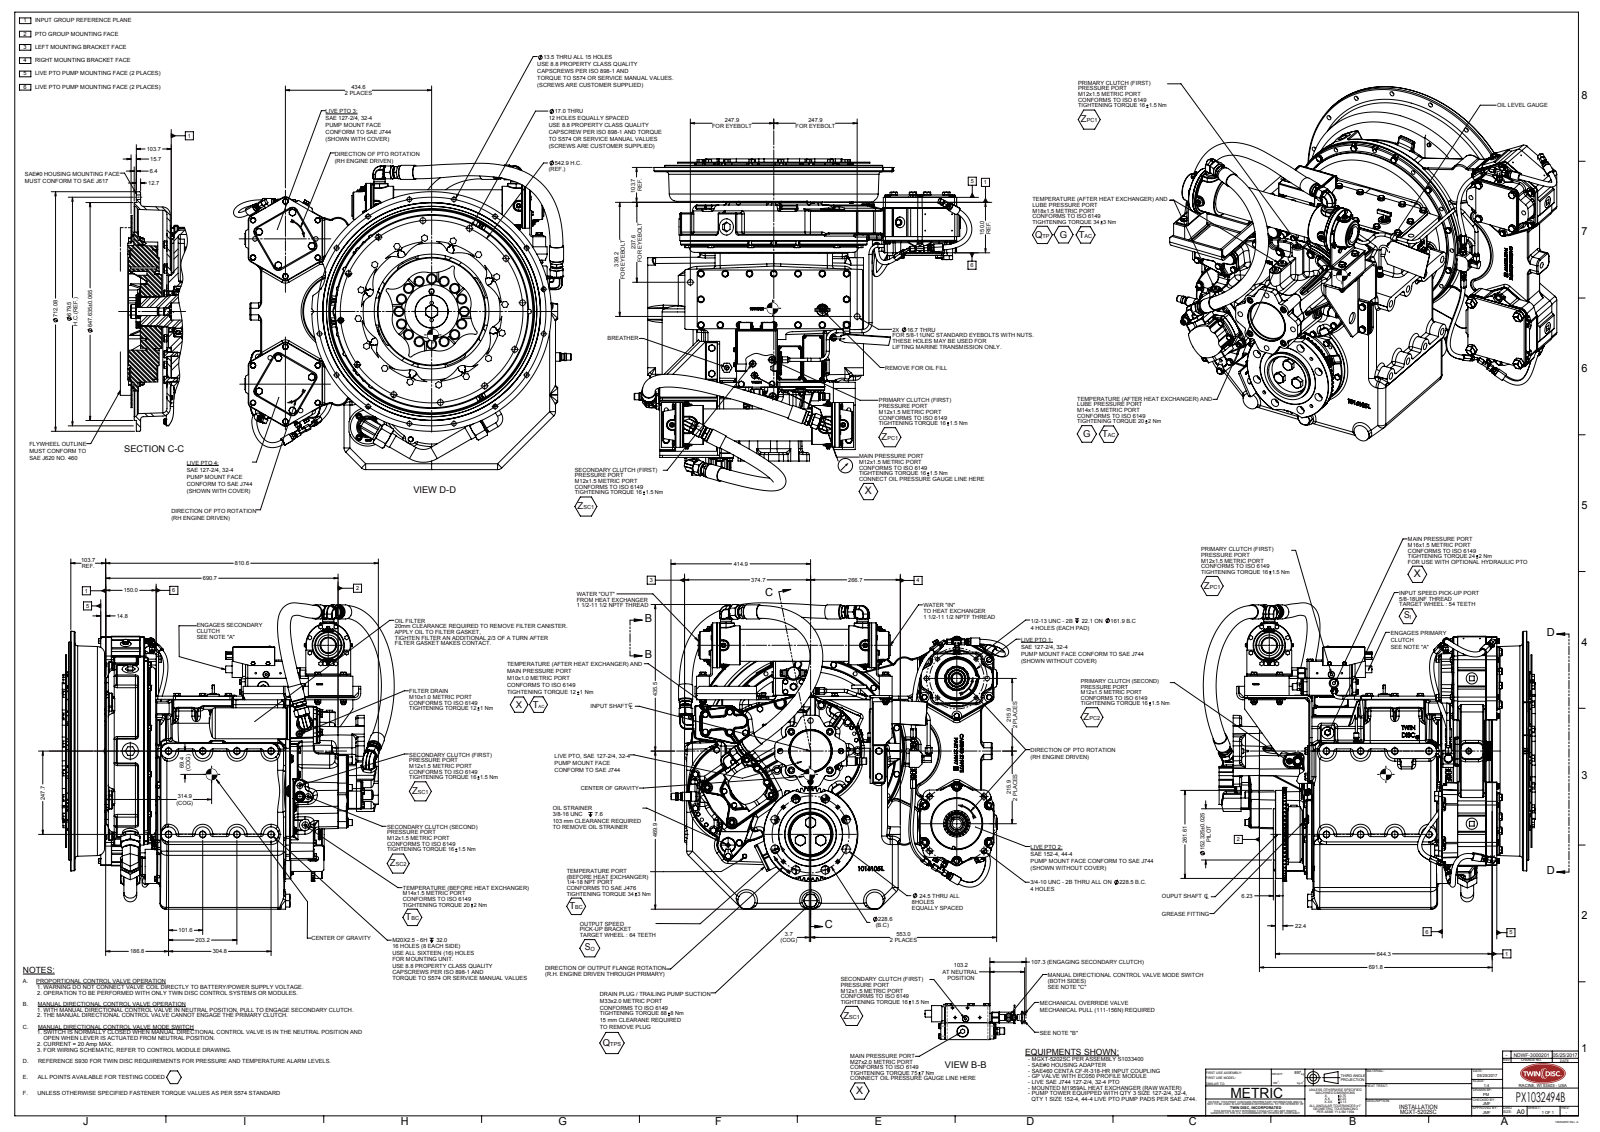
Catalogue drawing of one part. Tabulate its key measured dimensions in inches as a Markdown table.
| quantity | value |
| --- | --- |
| part name | PX1032494B |
| STEP written by | SolidWorks 2015 (AUTOMOTIVE_DESIGN) |
| units | inches |
| bodies | 0 solids, 5859 faces (2665 planar, 1454 cylindrical, 1740 other) |
| overall size | 51.237 × 38.85 × 35.846 |
| round holes (diameter × count) | 0.531 × 16, 0.787 × 13, 0.669 × 12, 0.965 × 8, 0.394 × 7, 0.469 × 7, 0.368 × 5, 0.531 × 5, 0.656 × 5, 0.63 × 4, 0.75 × 4, 0.709 × 3 |
| round bosses / shafts (diameter × count) | 0.787 × 21, 0.945 × 16, 0.62 × 10, 3.189 × 7, 1.181 × 7, 0.743 × 7, 1.5 × 6, 0.709 × 6 |
| partial cylindrical surfaces (radius × count) | 0.12 × 110, 0.25 × 90, 1.824 × 77, 0.118 × 60, 0.31 × 53, 0.472 × 46, 0.06 × 36, 0.5 × 32 |
| main face-to-face distances | 21.702, 0.016, 21.687, 22.084, 22.069, 0.382, 0.25, 26.285, 26.269, 4.583 |
| hole center spacings | 4.5, 6.364, 1.756, 3.444, 5, 7.483, 8.315, 8.827 |
